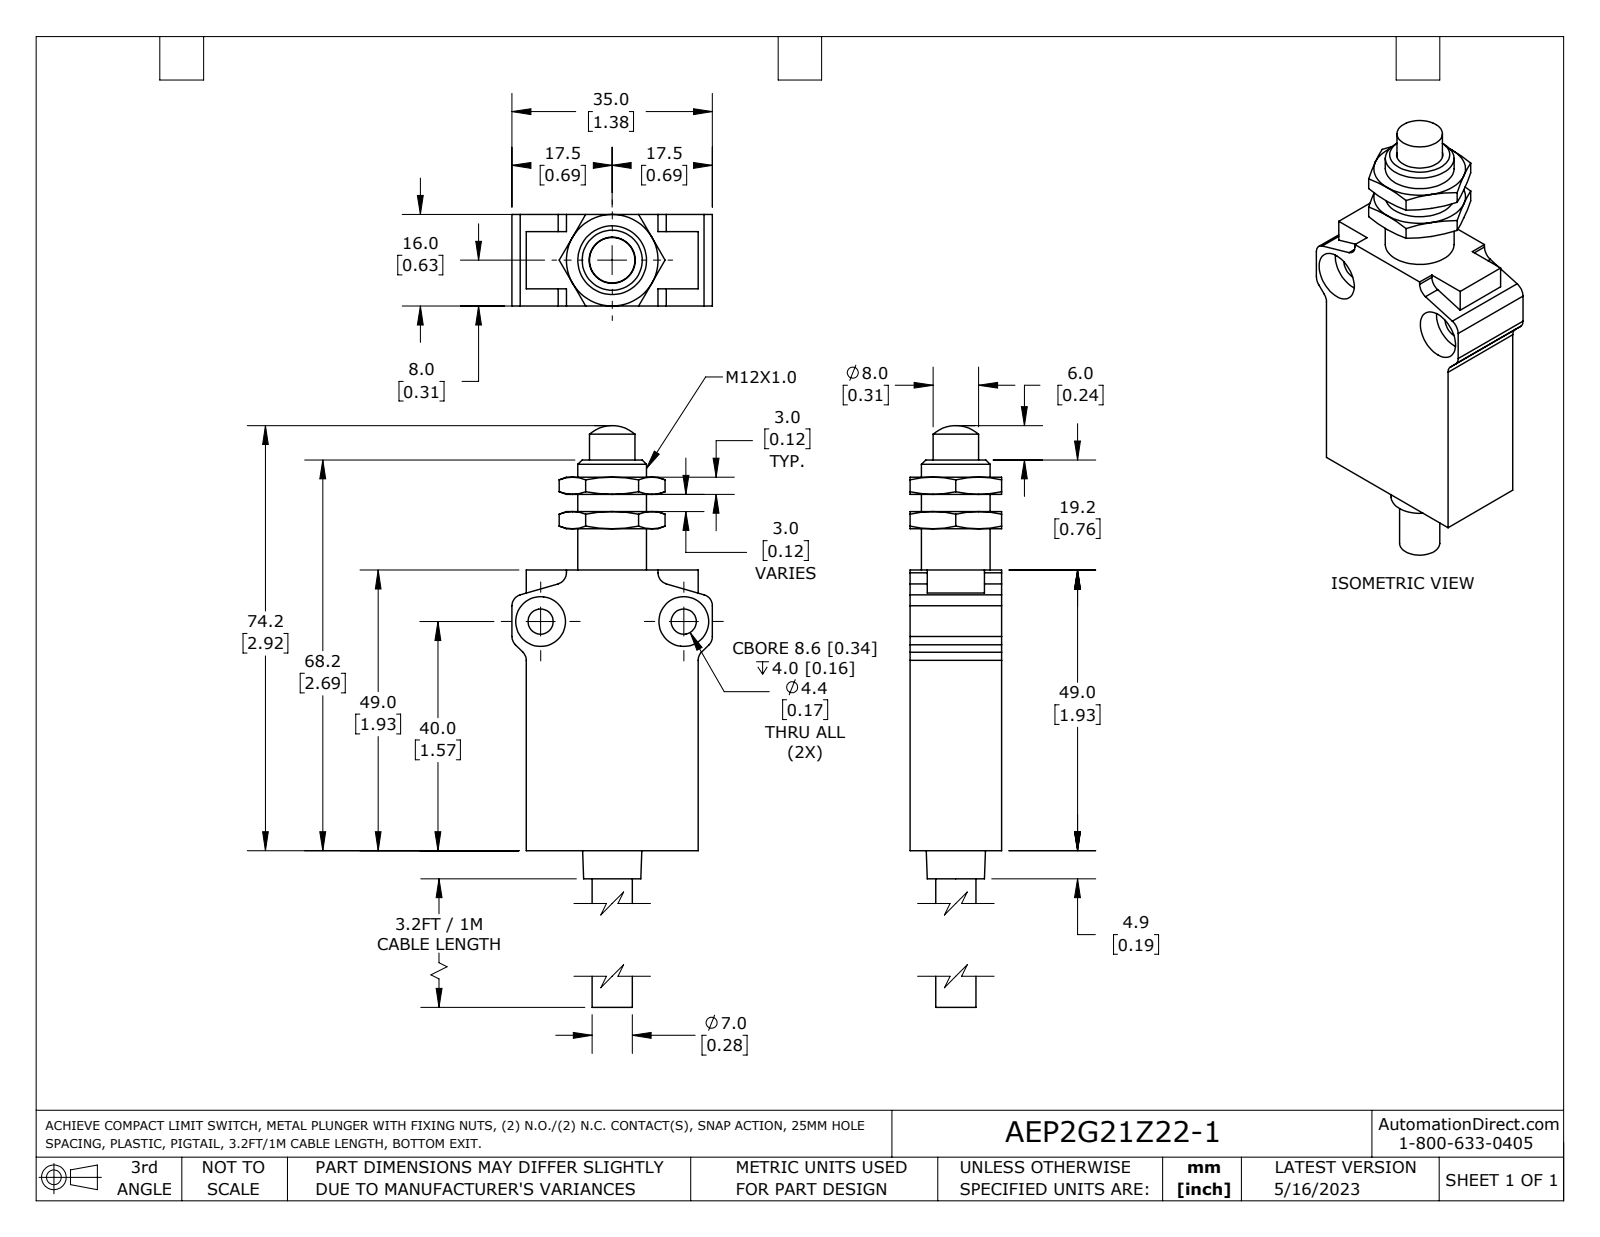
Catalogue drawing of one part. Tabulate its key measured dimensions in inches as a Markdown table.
| quantity | value |
| --- | --- |
| part name | AEP2G21Z22-1 |
| STEP written by | SolidWorks 2021 (AUTOMOTIVE_DESIGN) |
| units | inches |
| bodies | 3 solids, 118 faces (60 planar, 27 cylindrical, 31 other) |
| overall size | 3.508 × 1.378 × 0.63 |
| volume | 1.61 in³ |
| surface area | 14.72 in² |
| round holes (diameter × count) | 0.173 × 2, 0.343 × 2, 0.317 × 1, 0.472 × 1 |
| round bosses / shafts (diameter × count) | 0.313 × 1, 0.276 × 1 |
| partial cylindrical surfaces (radius × count) | 0.079 × 8, 0.256 × 1 |
| main face-to-face distances | 0.63, 1.181, 0.118, 1.929, 0.472, 0.236, 0.354, 0.157, 0.098, 1.28 |
| hole center spacings | 0.984 |
